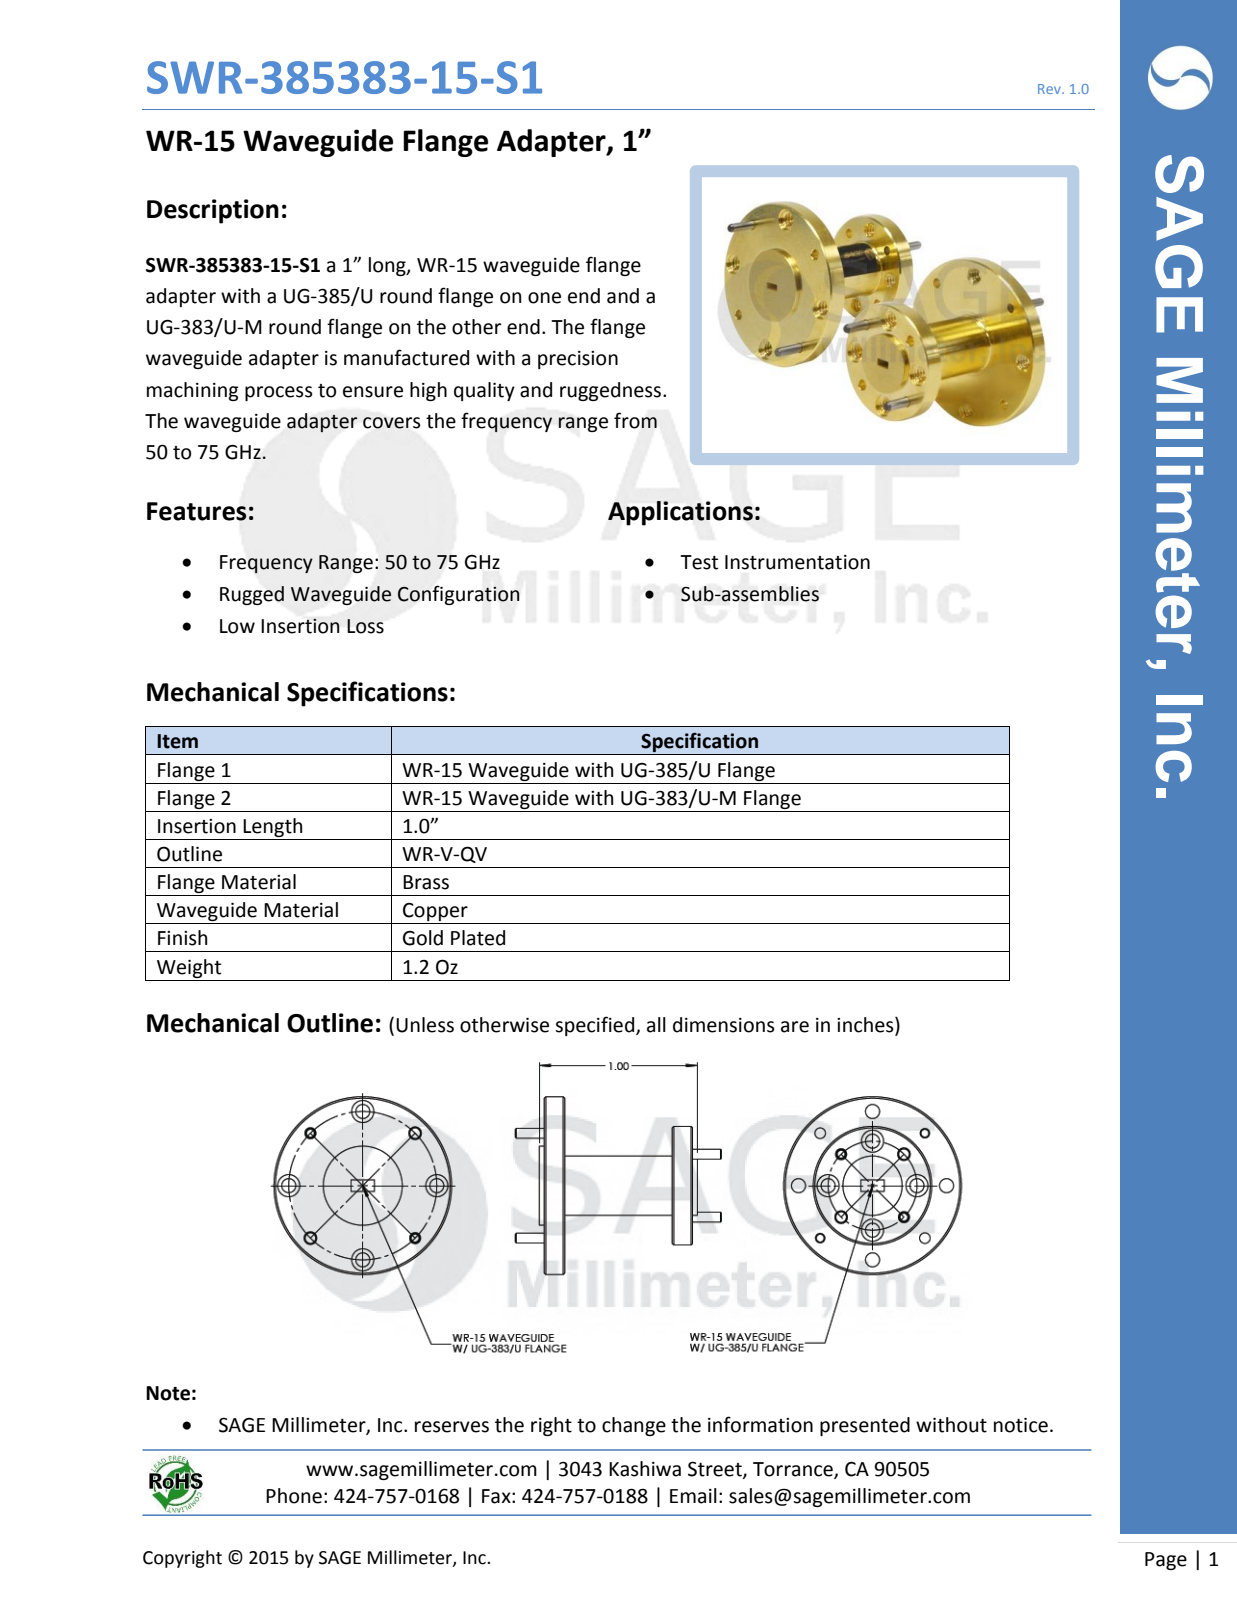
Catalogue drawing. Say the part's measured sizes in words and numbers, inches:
The part is named "WR-V-QV". Its 3-D file was written by "SolidWorks 2013 (CONFIG_CONTROL_DESIGN)". It is 5 solids with 132 faces: 26 planar, 66 cylindrical and 40 other. Overall it measures 1.305 by 1.125 by 1.125 inches. Its volume is 0.252 cubic inches and its surface area 5.284 square inches. Round holes: 8 of diameter 0.089, 8 of diameter 0.14, 4 of diameter 0.06, 4 of diameter 0.067. Round bosses or shafts: 4 of diameter 0.063, 1 of diameter 1.125, 1 of diameter 0.75, 1 of diameter 0.5, 1 of diameter 0.375. The main face-to-face distances are 0.13, 0.81, 0.68, 0.94, 0.03, 0.16, 0.84, 0.97, 0.074, 1. The hole center spacings are 0.335, 0.547, 0.215, 0.359, 0.696, 0.697, 0.75, 0.866.
